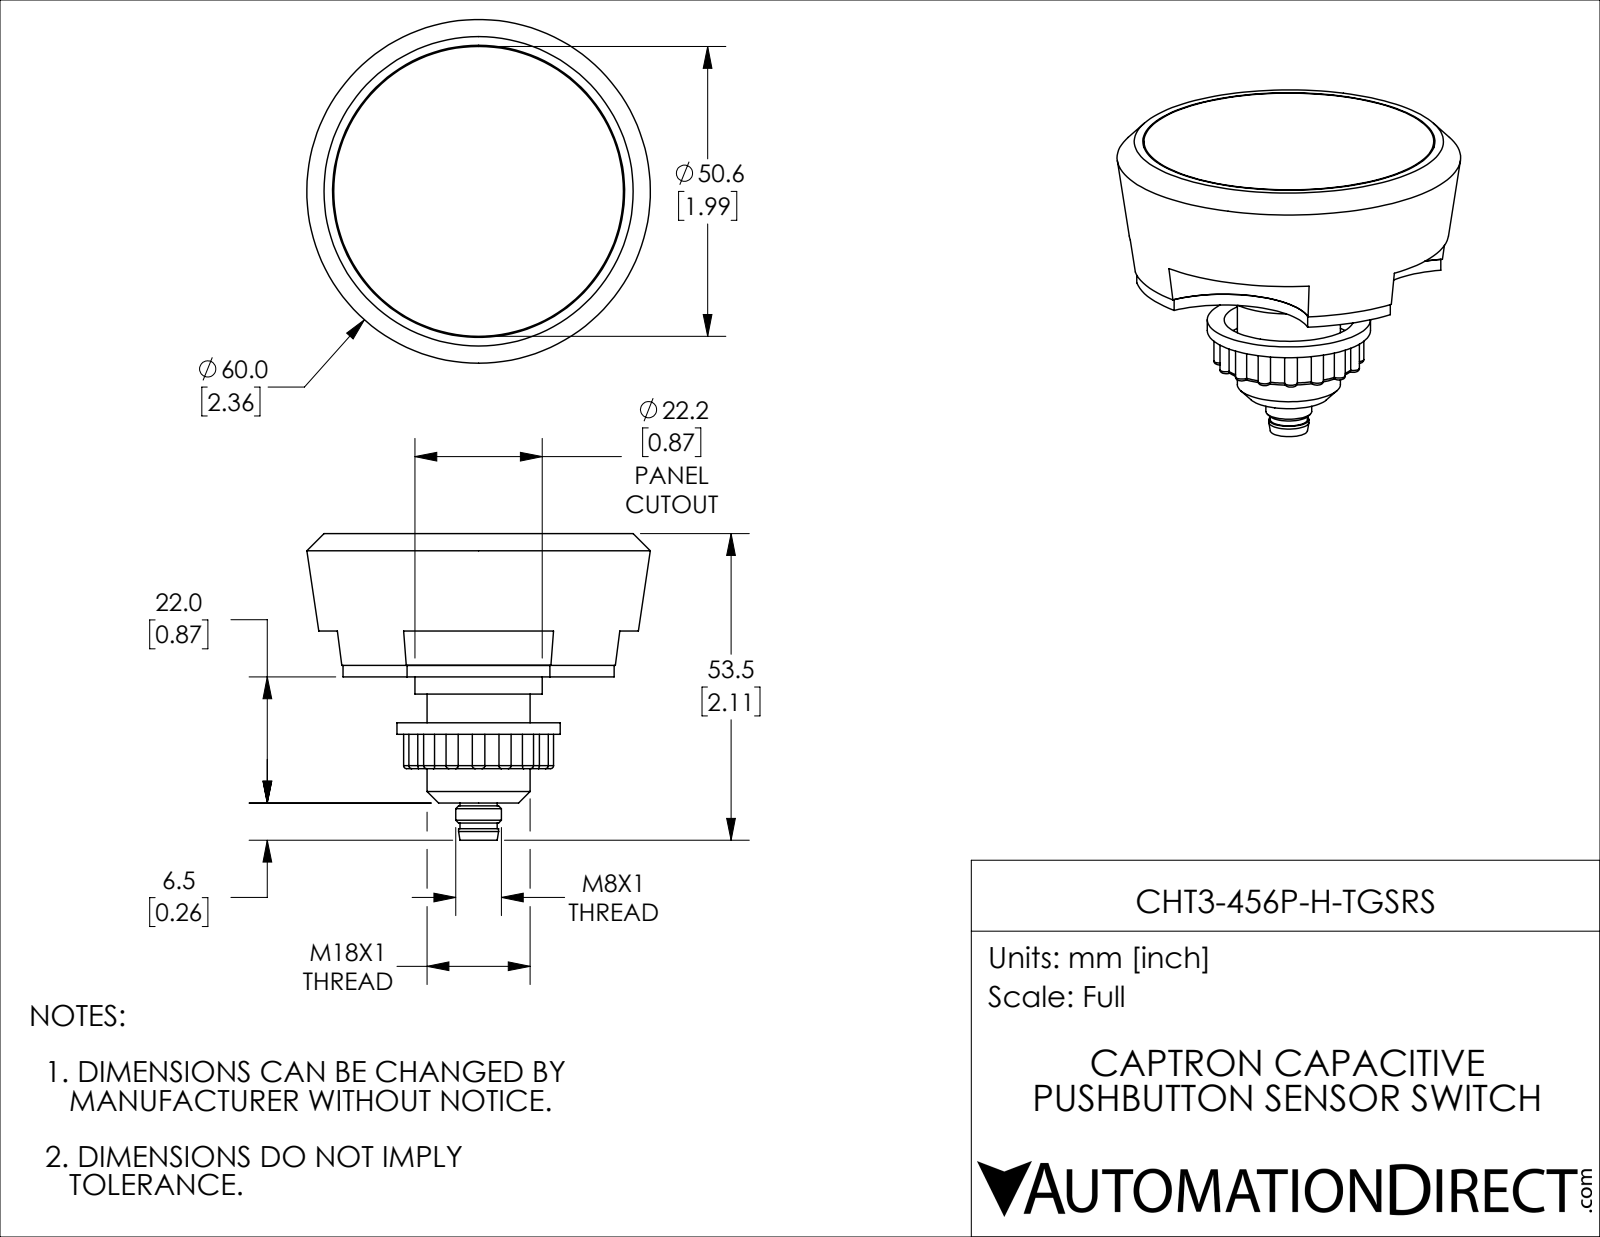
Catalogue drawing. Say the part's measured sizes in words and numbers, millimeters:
The part is named "CHT3-456P-H-TGSRS". Its 3-D file was written by "SolidWorks 2019 (CONFIG_CONTROL_DESIGN)". It is 9 solids with 197 faces: 27 planar, 95 cylindrical and 75 other. Overall it measures 60 by 60 by 53.5 millimeters. Its volume is 63 958 cubic millimeters and its surface area 20 586 square millimeters. Round holes: 1 of diameter 6, 1 of diameter 17, 1 of diameter 22.6, 1 of diameter 51. Round bosses or shafts: 4 of diameter 1, 1 of diameter 50.6, 1 of diameter 28.5, 1 of diameter 22.2, 1 of diameter 18, 1 of diameter 8, 1 of diameter 7, 1 of diameter 6.5. Partial cylindrical surfaces (rounded edges, fillets, slot ends): 16 of radius 1.1, 4 of radius 15, 1 of radius 12, 1 of radius 26.75. The main face-to-face distances are 23, 20.2, 2.8, 0.5, 20.7, 2.3, 2, 8, 22.2, 22.7.
